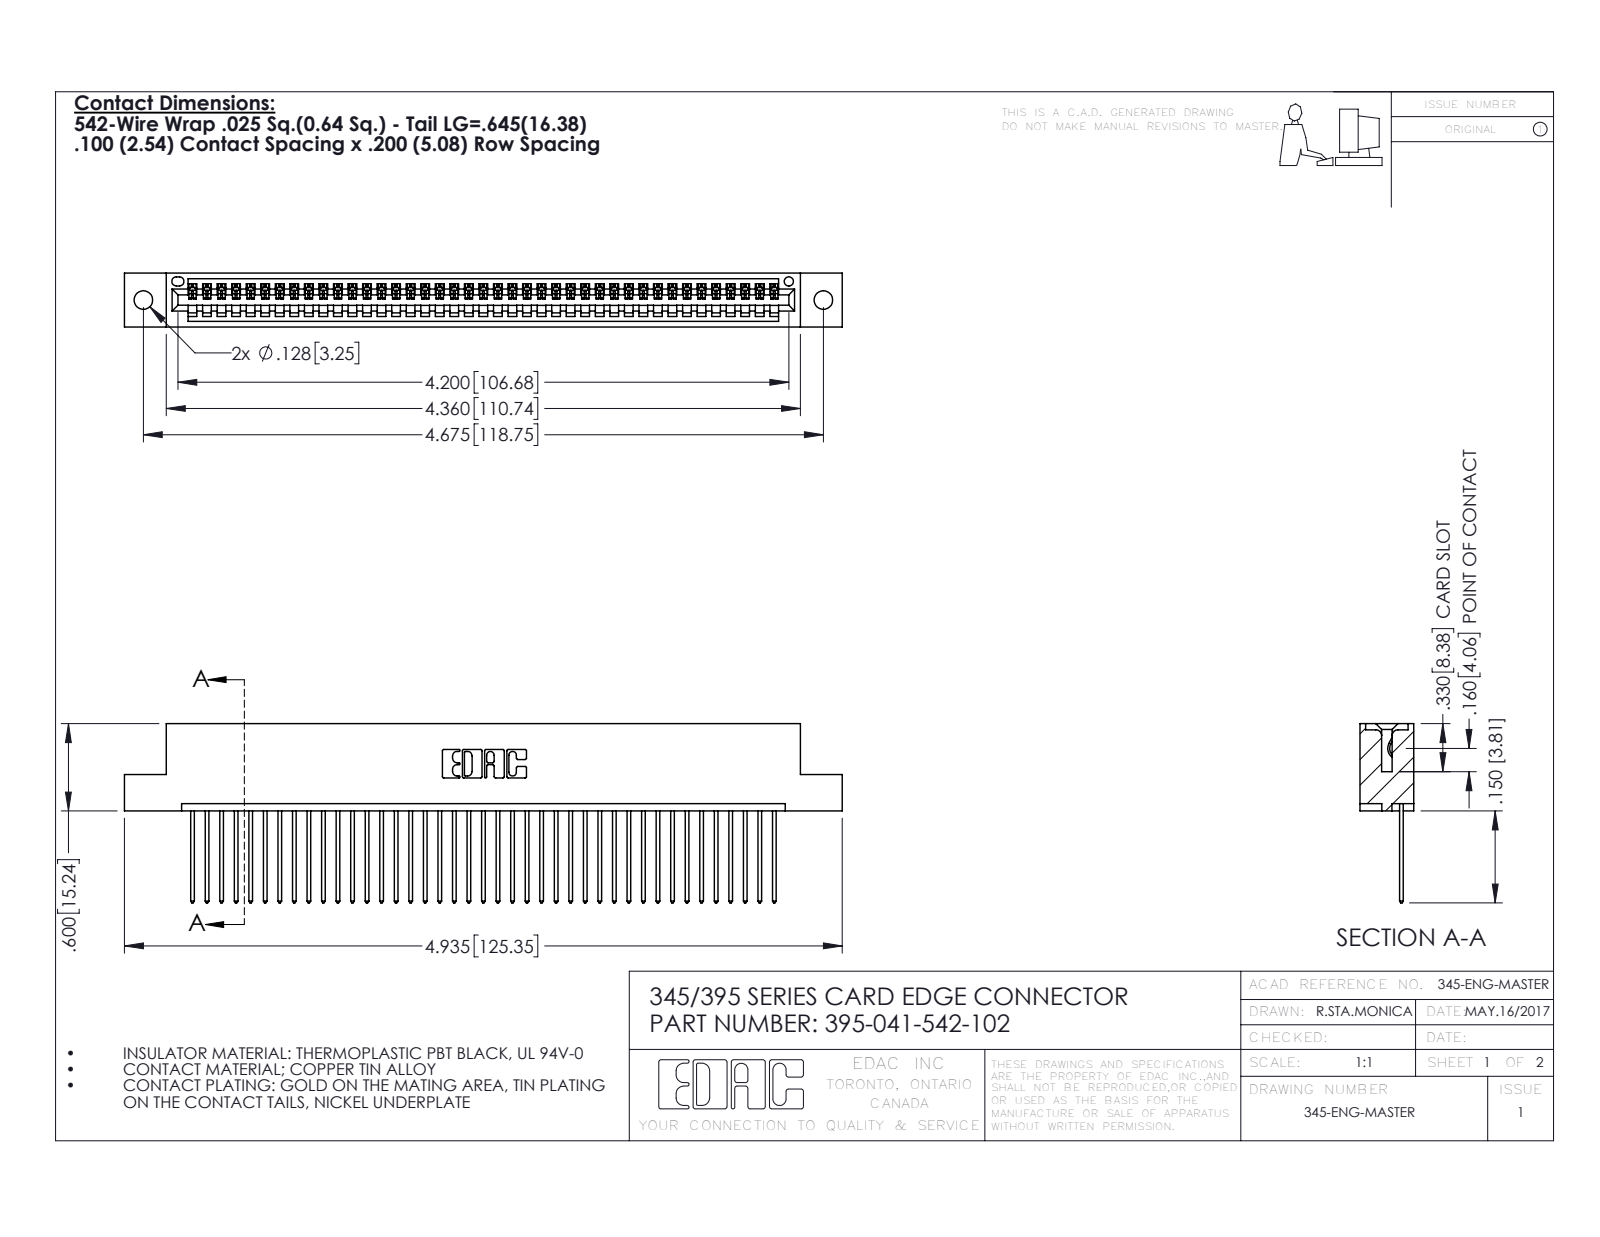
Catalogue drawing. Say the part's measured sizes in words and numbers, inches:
The part is named "345-292-001_345-293-142; 345 Part_Flush Mounting Lugs - 0.128 Dia; 395-041-542-102". Its 3-D file was written by "SolidWorks 2016 (CONFIG_CONTROL_DESIGN)". It is 42 solids with 2504 faces: 1720 planar, 784 cylindrical and 0 other. Overall it measures 4.935 by 1.232 by 0.37 inches. Its volume is 0.729 cubic inches and its surface area 25.07 square inches. Round holes: 2 of diameter 0.128, 1 of diameter 0.064. Partial cylindrical surfaces (rounded edges, fillets, slot ends): 82 of radius 0.006, 82 of radius 0.01, 22 of radius 0.01, 6 of radius 0.007, 6 of radius 0.031, 3 of radius 0.026, 2 of radius 0.031, 2 of radius 0.04. The main face-to-face distances are 0.072, 0.298, 0.37, 0.098, 0.272, 0.025, 0.2, 0.225, 0.149, 0.072. The hole center spacings are 0.27, 4.439, 4.675.
